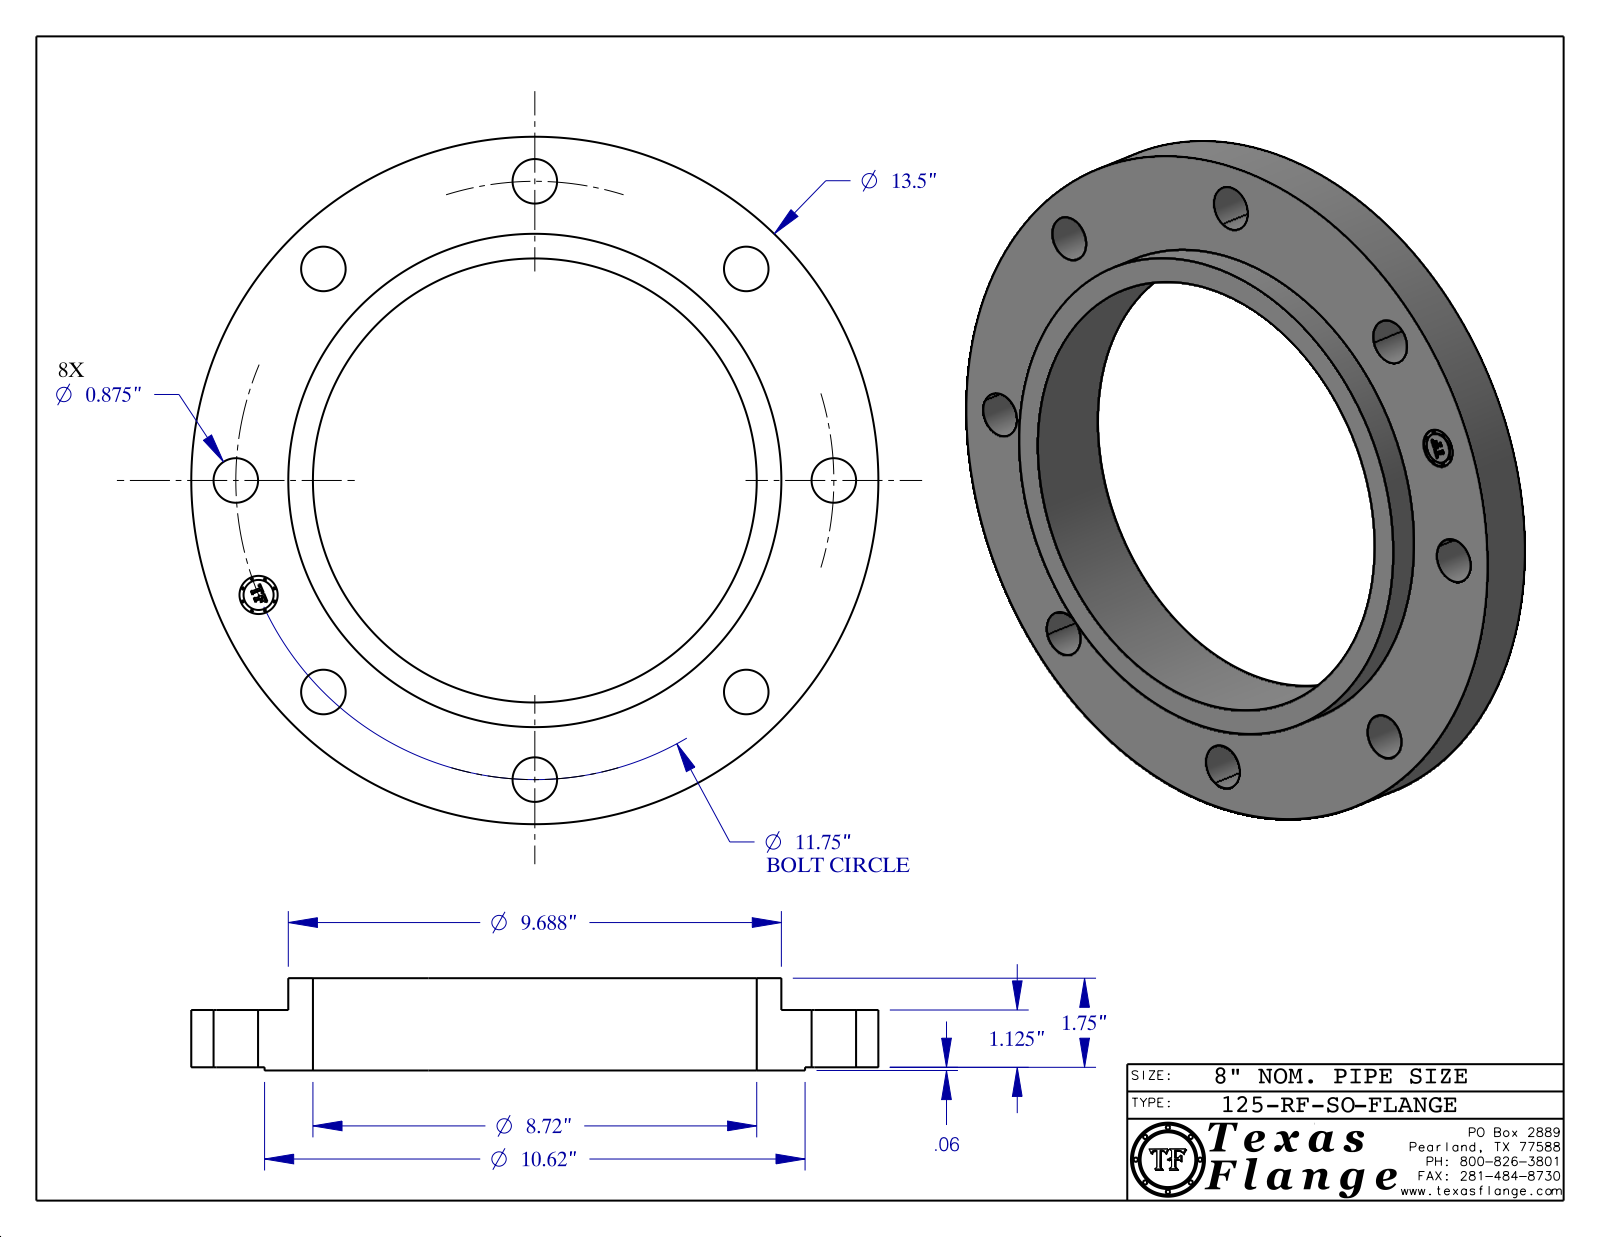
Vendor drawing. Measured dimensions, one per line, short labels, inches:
name: 125-RF-SO-B16.1
written by: CATIA V5 STEP AP214 (AUTOMOTIVE_DESIGN)
unit: in
bodies: 1 solid, 413 faces (369 planar, 44 cylindrical, 0 other)
size: 13.5 × 13.5 × 1.813
volume: 98.98 in³; area: 300.6 in²
holes: 8× ⌀0.875, 1× ⌀0.75, 1× ⌀8.72
bosses: 8× ⌀0.045, 1× ⌀13.5, 1× ⌀10.62, 1× ⌀9.688, 1× ⌀0.591
face distances: 1.125, 0.063, 1.187, 1.813, 1.75, 0.625, 1.172, 1.11, 0.015, 0.64
hole spacings: 5.875, 4.496, 8.309, 10.856, 11.75, 9.77, 2.292, 2.293
